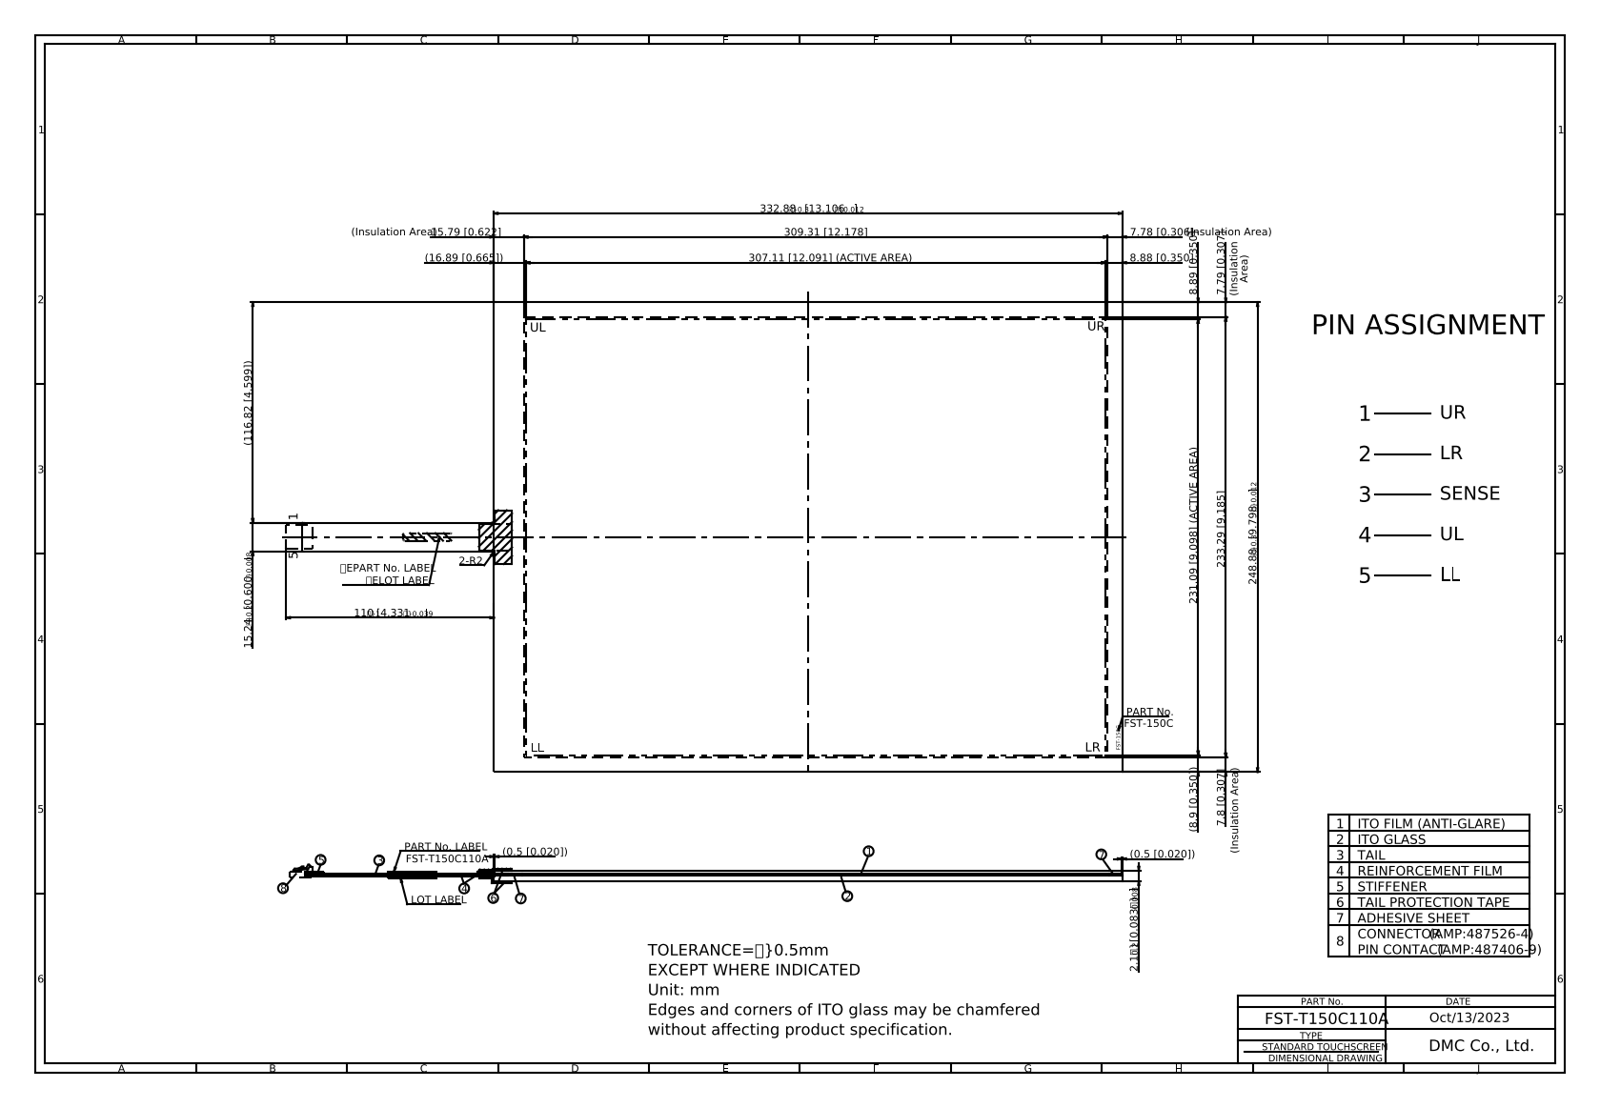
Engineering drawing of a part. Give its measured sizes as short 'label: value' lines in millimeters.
name: FST-T150C110A
written by: Autodesk Inventor 2020 (AUTOMOTIVE_DESIGN)
unit: mm
bodies: 1 solid, 43 faces (43 planar, 0 cylindrical, 0 other)
size: 509.47 × 348.43 × 3.15
volume: 167 312 mm³; area: 171 669 mm²
face distances: 2, 2.1, 1.8, 1.9, 248.88, 332.88, 0.65, 0.75, 0.85, 1.15
